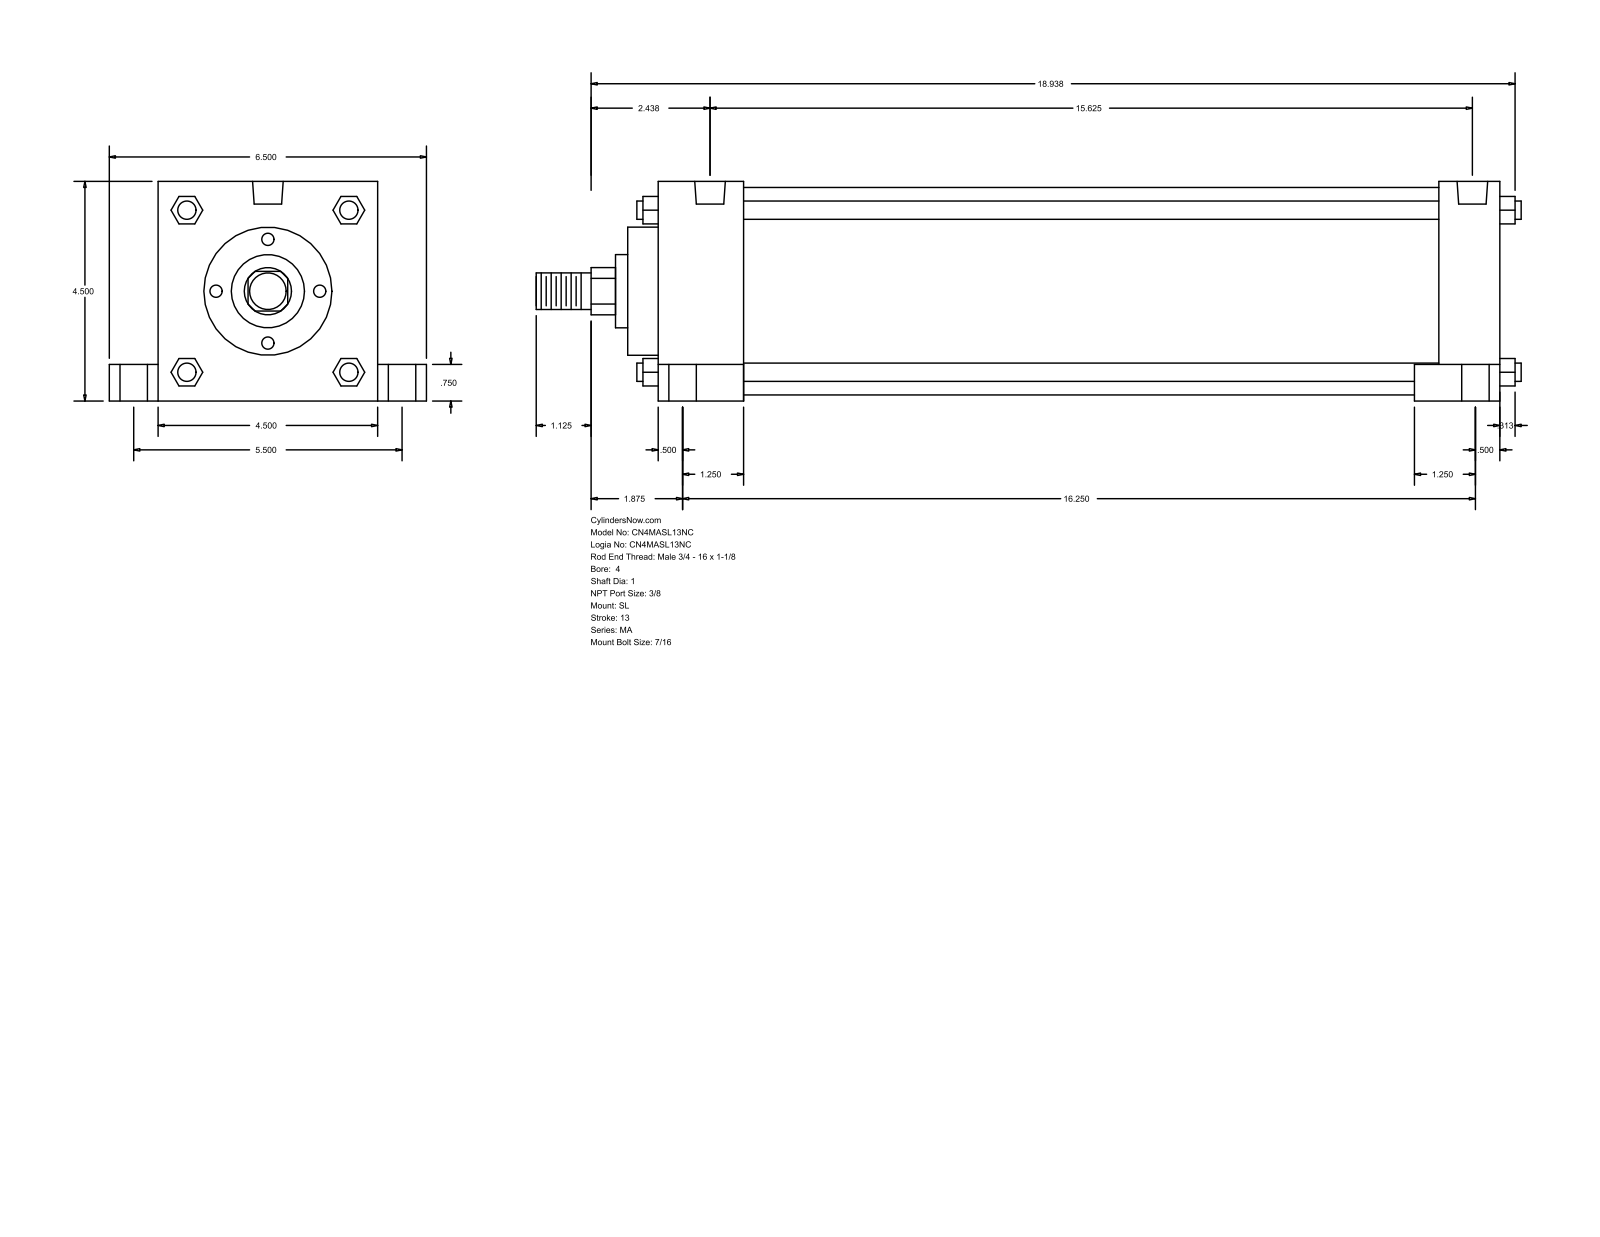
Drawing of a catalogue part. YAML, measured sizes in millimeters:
part_name: "MA_SL__0400_1"
step_written_by: "GSSL Pune (CONFIG_CONTROL_DESIGN)"
units: millimeters
bodies: {solids: 0, faces: 150, planar: 113, cylindrical: 37, other: 0}
overall_size: [512.76, 165.1, 114.3]
round_holes:
  - {diameter: 11.11, count: 4}
  - {diameter: 14.29, count: 4}
  - {diameter: 20.64, count: 4}
  - {diameter: 15.93, count: 2}
round_bosses_or_shafts:
  - {diameter: 9.53, count: 4}
  - {diameter: 107.95, count: 1}
  - {diameter: 66.67, count: 1}
  - {diameter: 38.1, count: 1}
  - {diameter: 25.4, count: 1}
  - {diameter: 19.05, count: 1}
partial_cylinders:
  - {radius: 12.29, count: 1}
face_to_face_distances: [114.3, 438.15, 44.46, 393.69, 406.4, 361.94, 31.75, 25.4, 139.7, 454.02]
hole_center_spacings: [69.87, 70.14, 71.3, 72.4, 139.7, 387.35, 399.86, 404.55]
